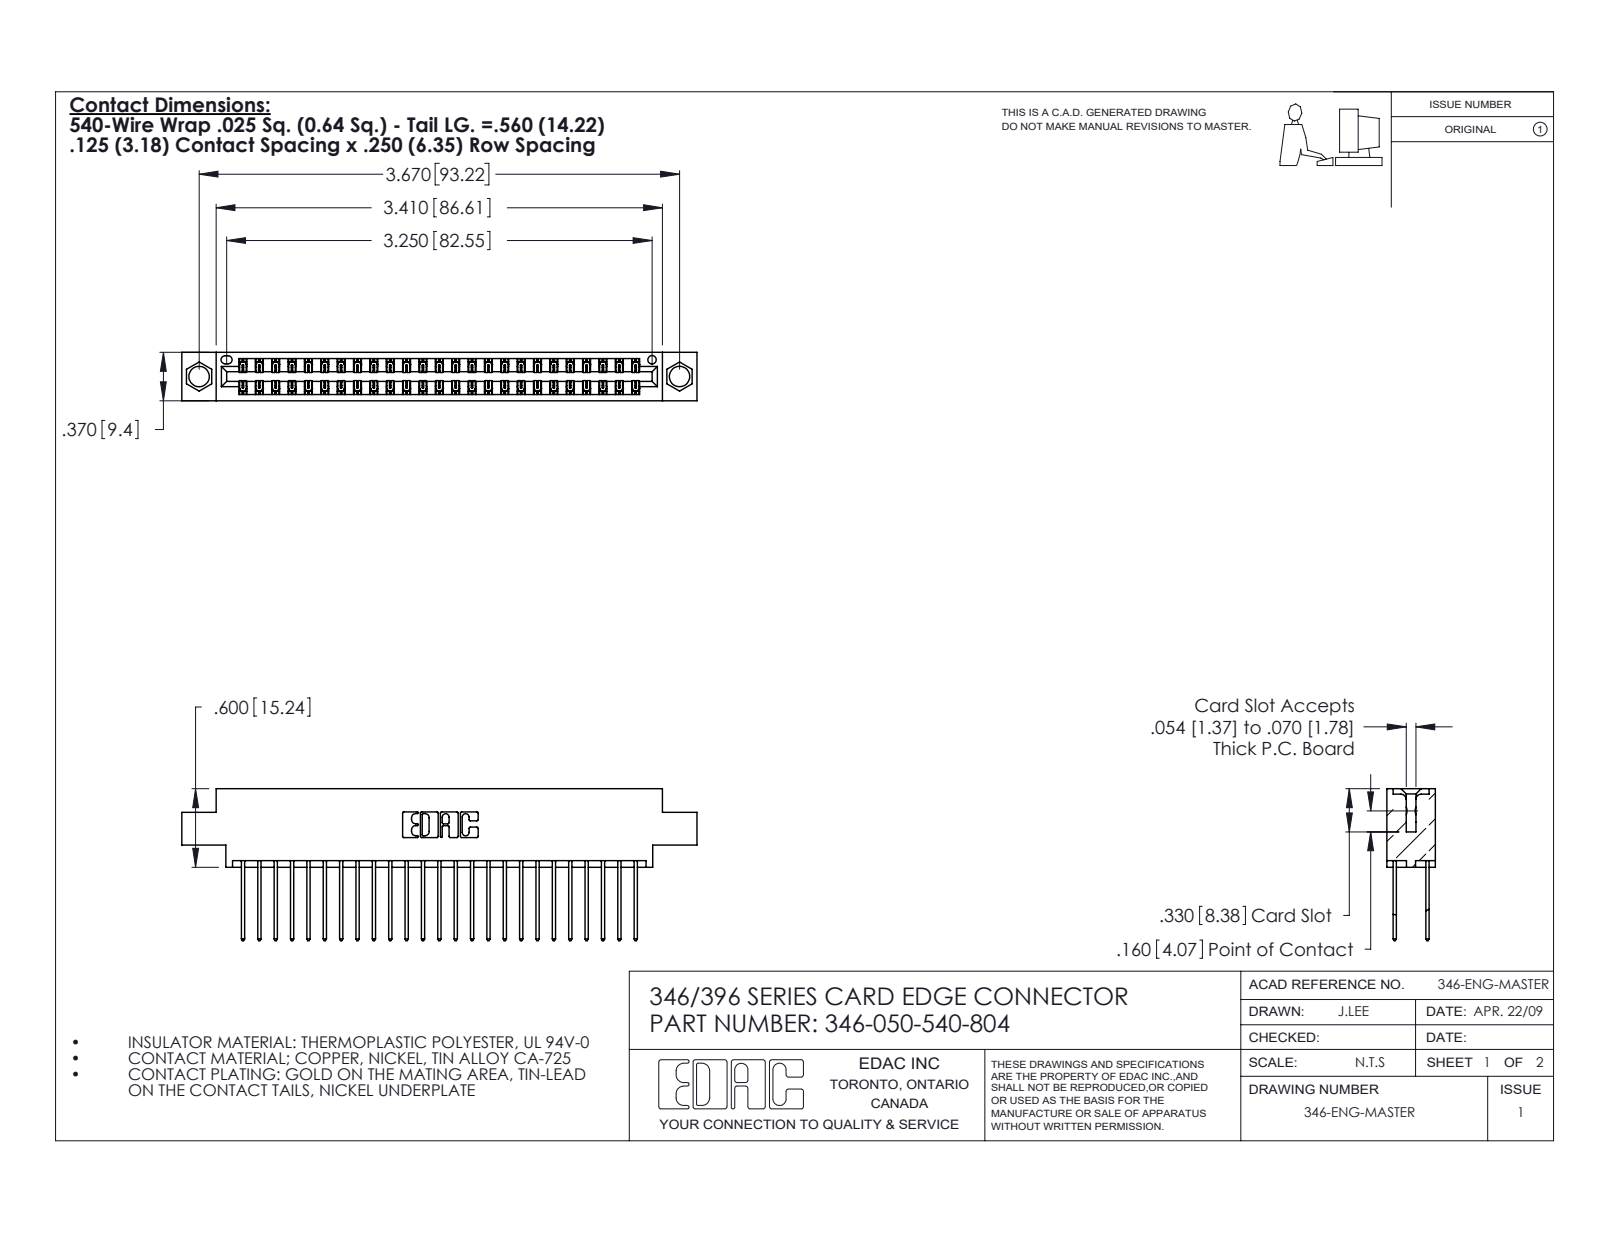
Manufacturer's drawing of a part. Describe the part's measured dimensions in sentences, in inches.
The part is named "346 Part_0.170 Offset - 0.156 Dia-TH; 346-050-540-804; 345-292-001_345-293-140". Its 3-D file was written by "SolidWorks 2020 (CONFIG_CONTROL_DESIGN)". It is 51 solids with 2740 faces: 1844 planar, 896 cylindrical and 0 other. Overall it measures 3.935 by 1.16 by 0.37 inches. Its volume is 0.582 cubic inches and its surface area 21.35 square inches. Round holes: 2 of diameter 0.156, 1 of diameter 0.064. Partial cylindrical surfaces (rounded edges, fillets, slot ends): 75 of radius 0.006, 50 of radius 0.01, 22 of radius 0.01, 6 of radius 0.007, 6 of radius 0.031, 3 of radius 0.026, 2 of radius 0.014, 2 of radius 0.022. The main face-to-face distances are 0.048, 0.322, 0.25, 0.37, 0.072, 0.298, 0.025, 0.275, 0.222, 0.148. The hole center spacings are 0.246, 3.462, 3.67.
